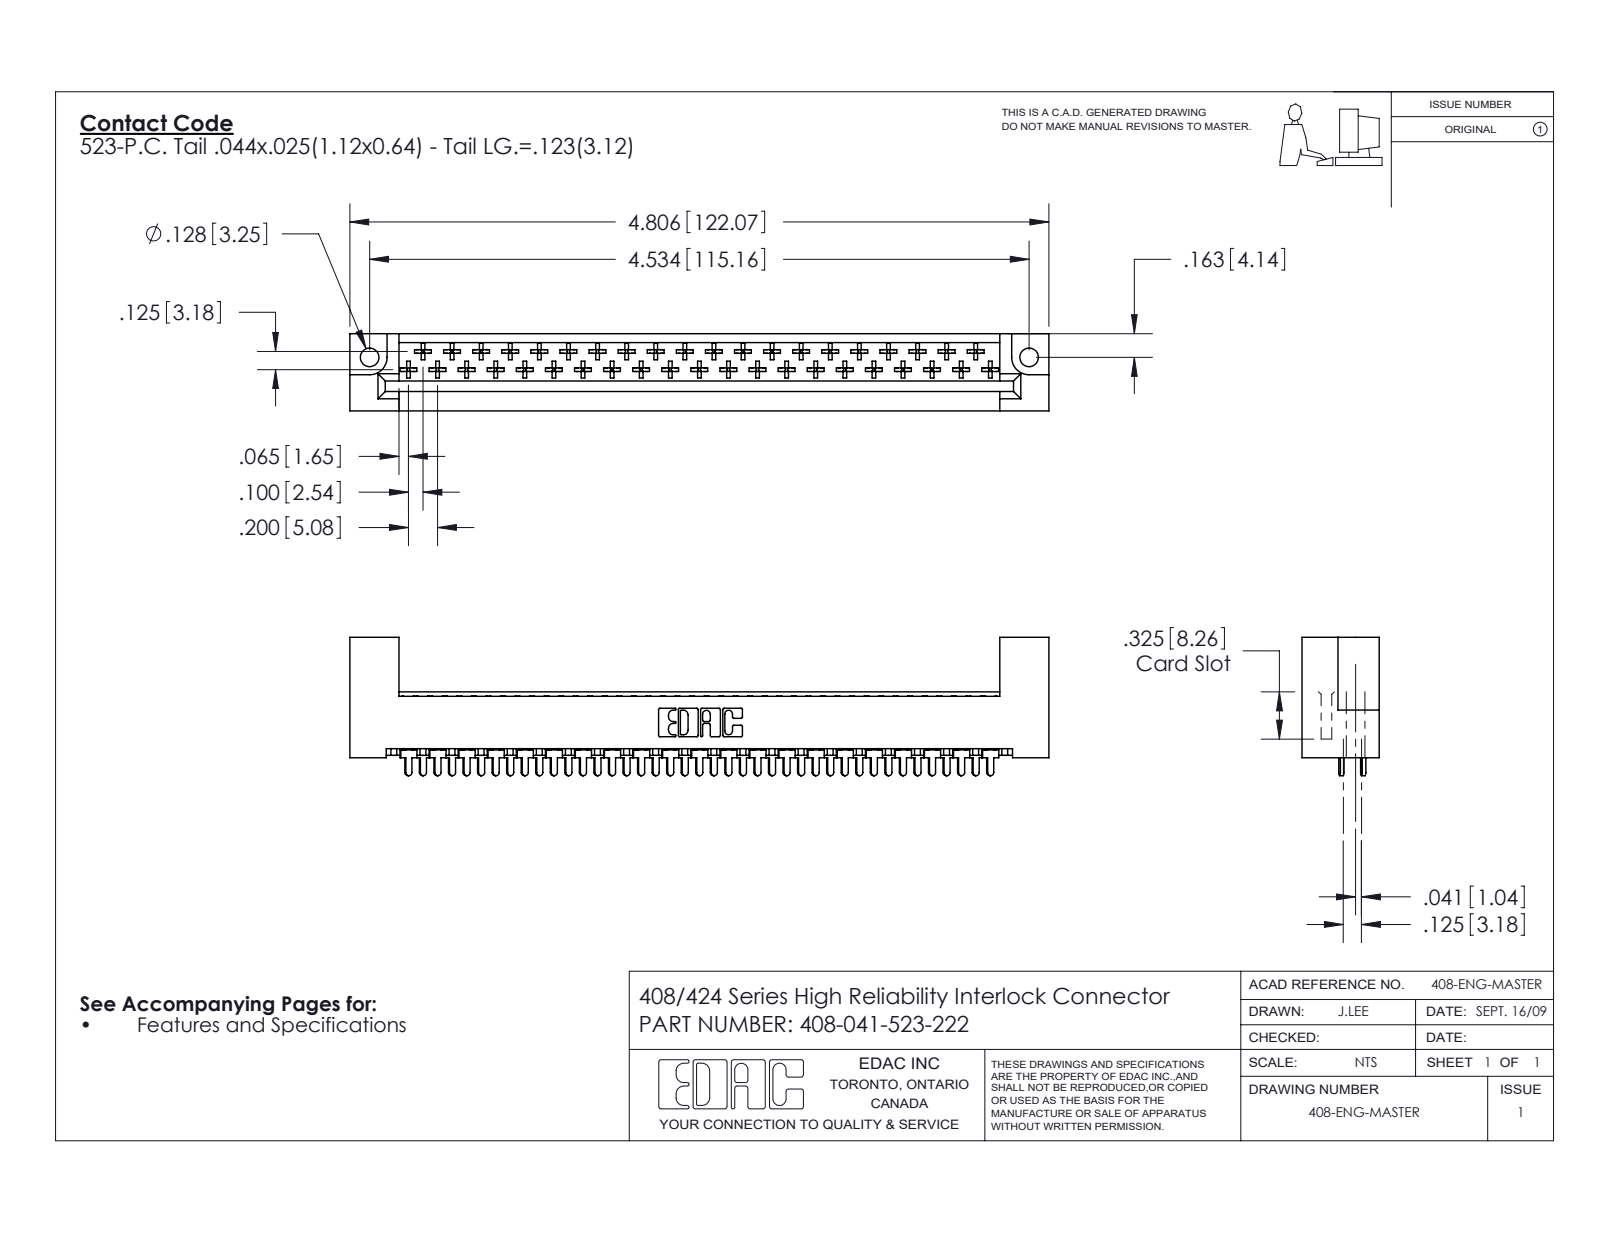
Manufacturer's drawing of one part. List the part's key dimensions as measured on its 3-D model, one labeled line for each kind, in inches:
Part name (STEP PRODUCT): 408-290-001_408-290-123 - Top; 408-047-523-222; 408 Part_041 - 2; 408-290-001_408-290-123 - Bottom
STEP written by: SolidWorks 2016 (CONFIG_CONTROL_DESIGN)
Units: inches
Bodies: 42 solids, 2394 faces (1811 planar, 419 cylindrical, 164 other)
Overall size (bounding box): 4.806 × 0.951 × 0.531
Volume: 0.916 in³ · Surface area: 27.18 in²
Round holes (diameter × count): ⌀0.128 ×2
Partial cylindrical surfaces — rounded edges, fillets, slot ends (radius × count): R0.01 ×246, R0.02 ×43, R0.022 ×41, R0.01 ×22, R0.007 ×6, R0.031 ×6, R0.026 ×3, R0.12 ×2
Main face-to-face distances: 0.531, 0.125, 0.025, 0.1, 0.025, 0.361, 0.235, 0.259, 0.398, 0.217
Hole centre spacings: 4.534
